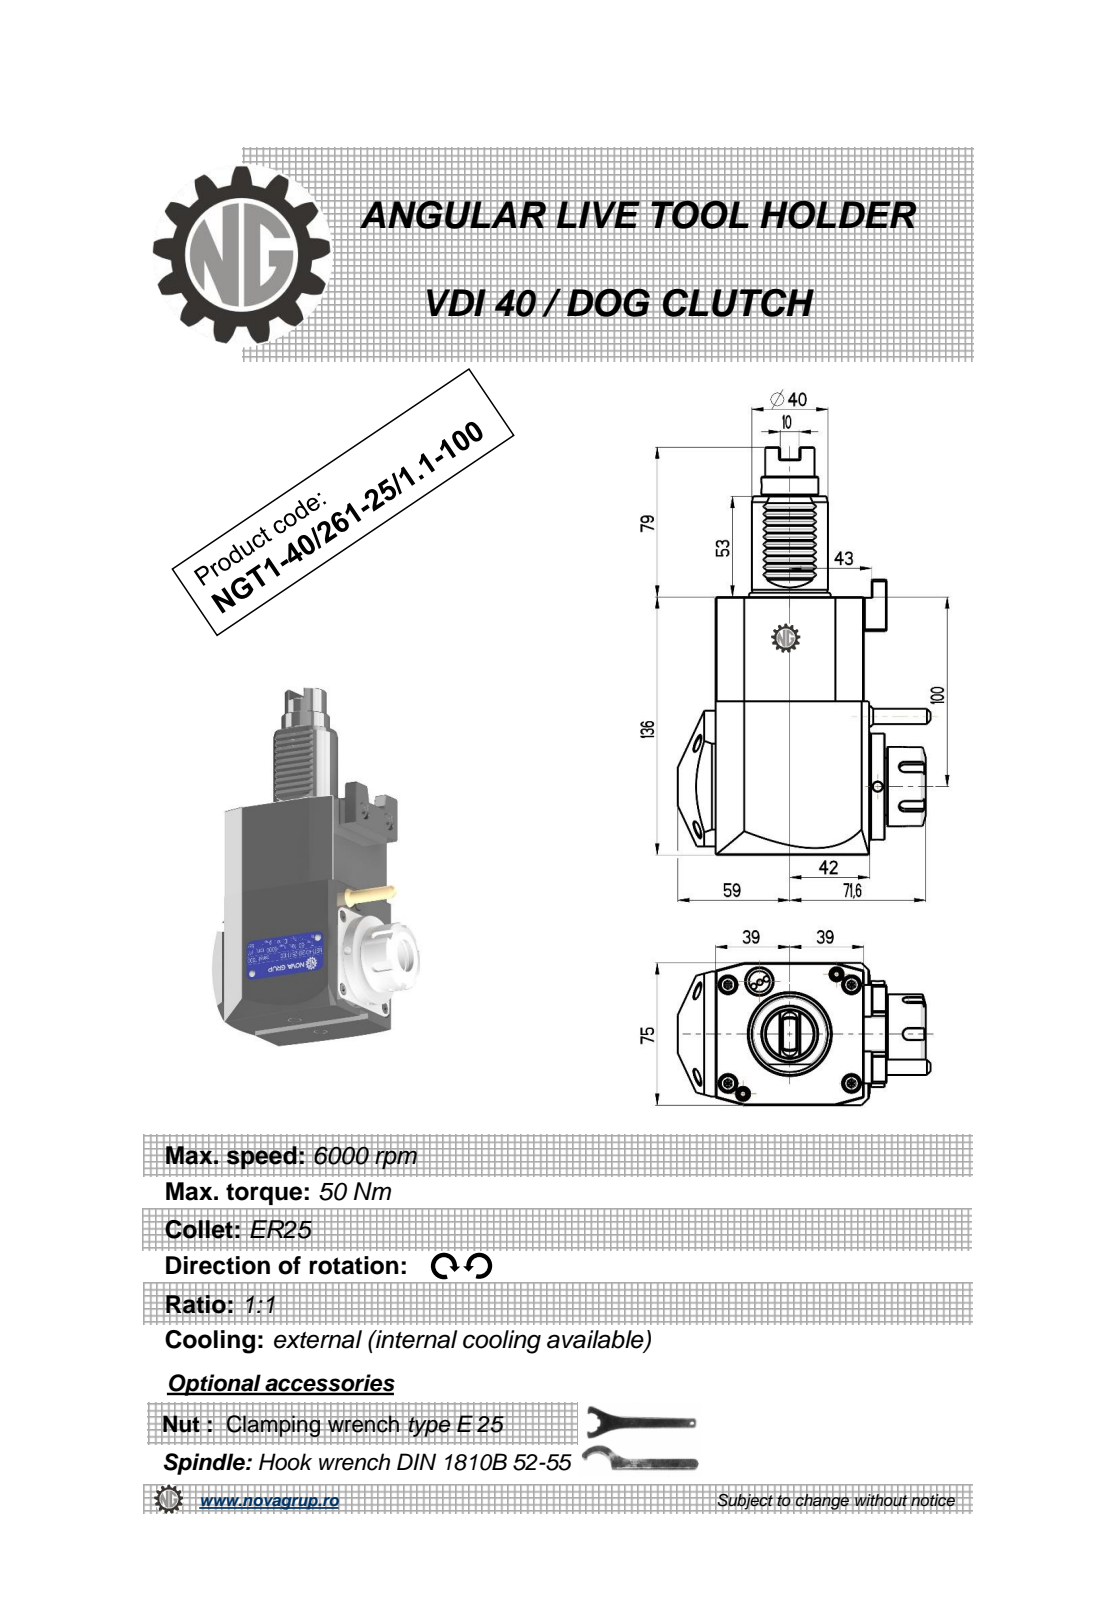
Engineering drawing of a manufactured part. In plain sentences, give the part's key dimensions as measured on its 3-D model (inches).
The part is named "NGT1_40_261_25_1_1_100". Its 3-D file was written by "PRO/ENGINEER BY PARAMETRIC TECHNOLOGY CORPORATION, 2010280 (CONFIG_CONTROL_DESIGN)". It is 1 solid with 400 faces: 199 planar, 74 cylindrical and 127 other. Overall it measures 8.465 by 5.242 by 2.953 inches. Its volume is 60.22 cubic inches and its surface area 118.3 square inches. Round holes: 3 of diameter 0.197, 1 of diameter 0.118, 1 of diameter 0.165, 1 of diameter 0.799. Round bosses or shafts: 1 of diameter 2.205, 1 of diameter 1.693, 1 of diameter 1.654, 1 of diameter 1.575, 1 of diameter 1.299, 1 of diameter 1.181, 1 of diameter 1.024, 1 of diameter 0.441. Partial cylindrical surfaces (rounded edges, fillets, slot ends): 10 of radius 0.012, 6 of radius 0.009, 6 of radius 0.01, 5 of radius 0.118, 3 of radius 0.02, 2 of radius 0.039, 1 of radius 0.492, 1 of radius 1.575. The main face-to-face distances are 2.953, 5.354, 3.071, 3.189, 0.118, 0.02, 0.315, 0.433, 3.342, 0.323. The hole center spacings are 1.611, 4.833, 6.24.
